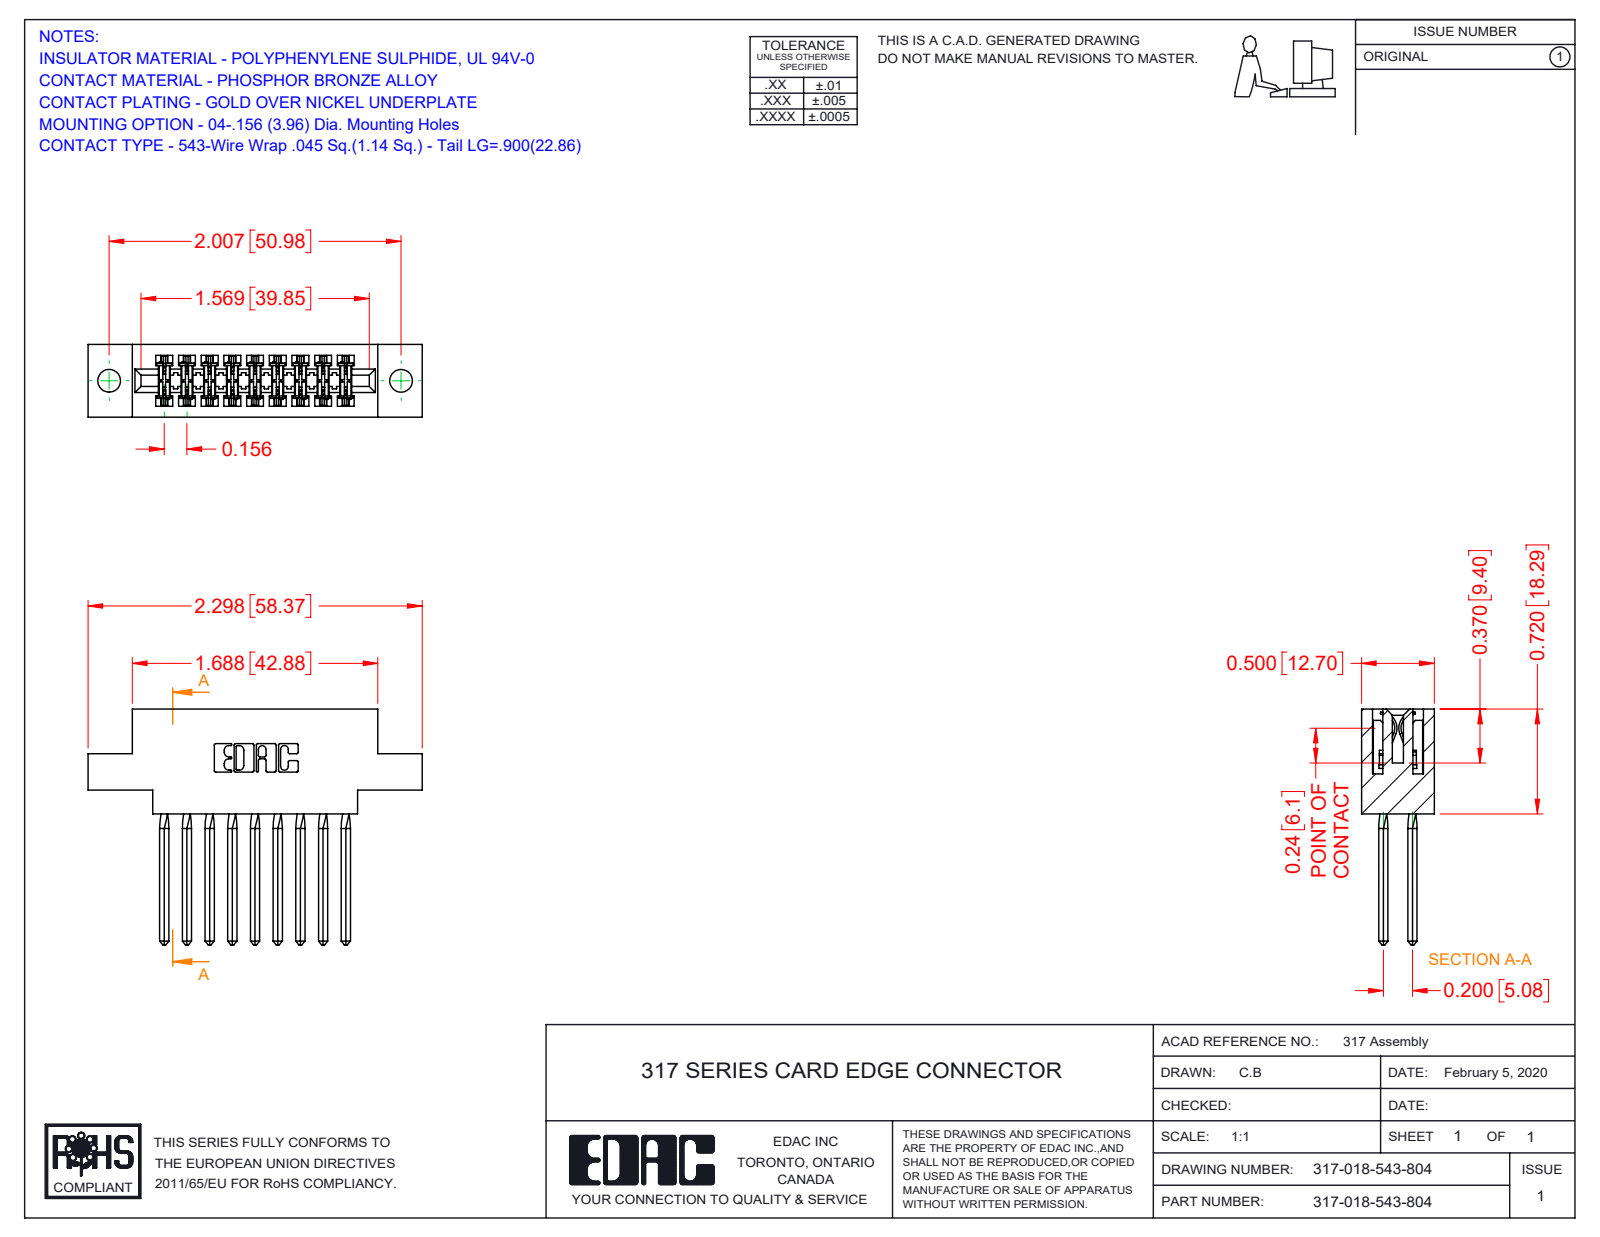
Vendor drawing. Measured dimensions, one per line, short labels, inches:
name: 317-290-001_543; 317 Part_.156 Dia - TH; 317-018-543-804
written by: SolidWorks 2016 (CONFIG_CONTROL_DESIGN)
unit: in
bodies: 19 solids, 1704 faces (1372 planar, 260 cylindrical, 72 other)
size: 2.298 × 1.62 × 0.5
volume: 0.53 in³; area: 18.14 in²
holes: 2× ⌀0.156
rounds: 36× R0.015, 22× R0.01, 6× R0.007, 6× R0.031, 3× R0.026, 2× R0.095, 2× R0.1, 2× R0.11
face distances: 0.5, 0.11, 0.075, 0.425, 0.22, 0.156, 0.331, 0.35, 0.116, 0.305
hole spacings: 2.007
